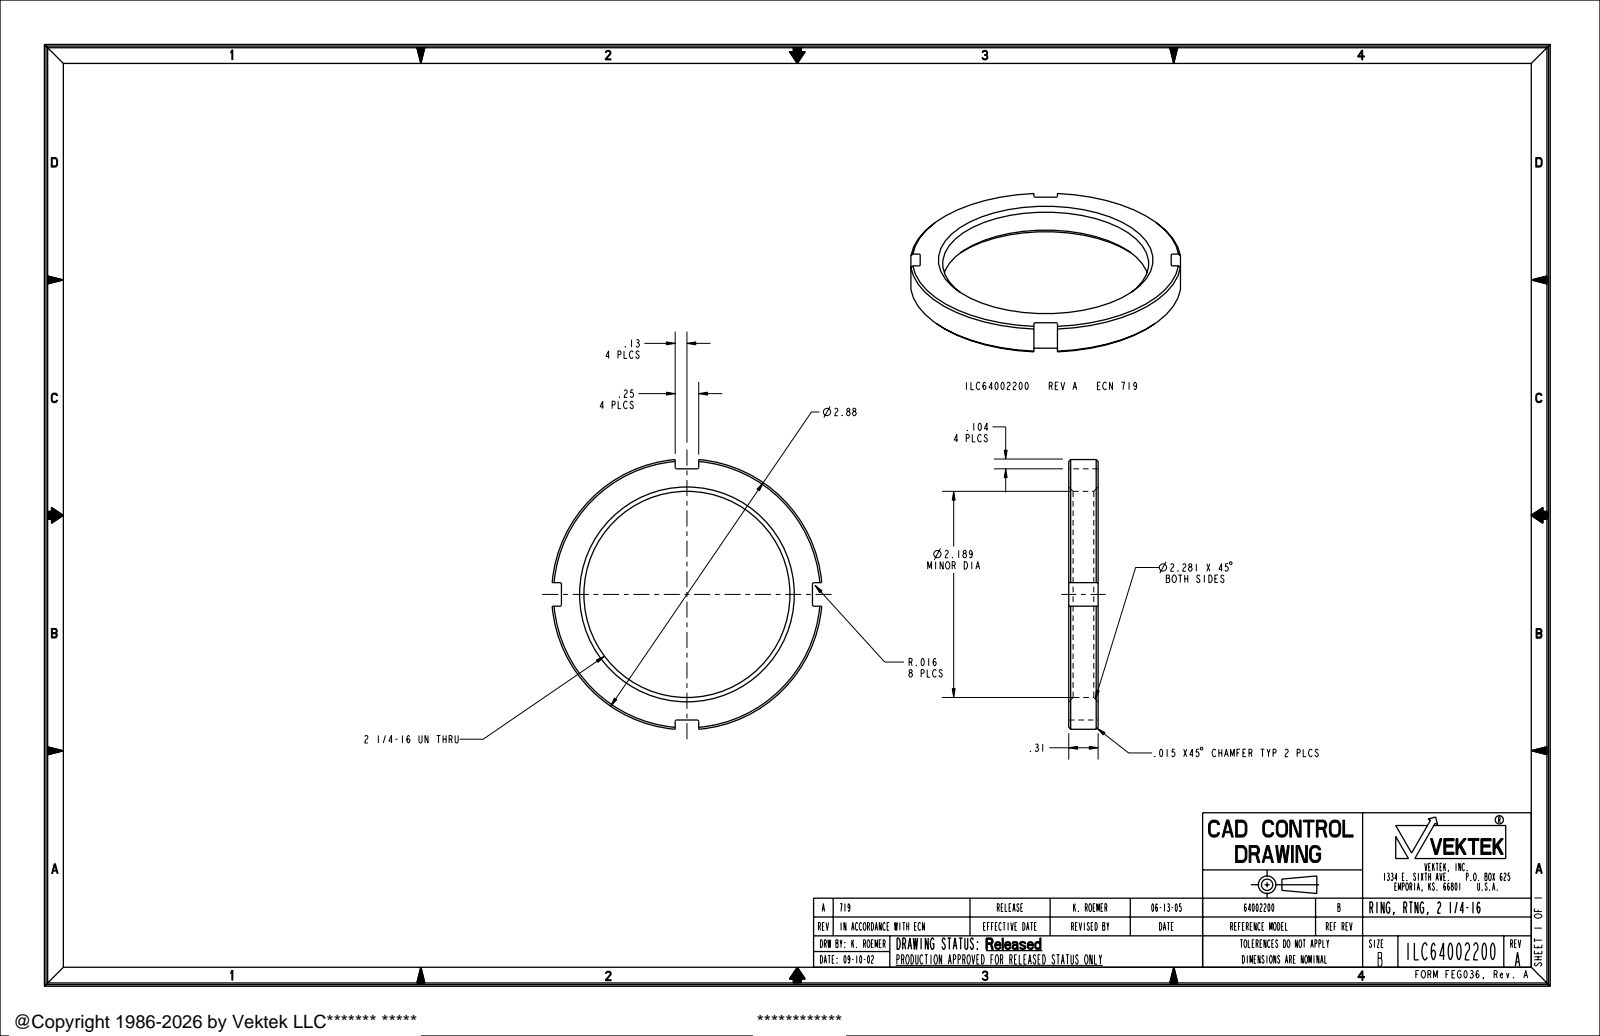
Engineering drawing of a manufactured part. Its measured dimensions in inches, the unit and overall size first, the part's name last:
Units: inches
Overall size (bounding box): 2.875 × 2.875 × 0.312
Round holes (diameter × count): ⌀2.189 ×1
Round bosses / shafts (diameter × count): ⌀2.875 ×1
Partial cylindrical surfaces — rounded edges, fillets, slot ends (radius × count): R0.016 ×8
Main face-to-face distances: 0.312, 1.209, 1.458, 2.667, 0.25
Volume: 0.801 in³ · Surface area: 9.883 in²
Bodies: 1 solid, 40 faces (14 planar, 14 cylindrical, 12 other)
Part name (STEP PRODUCT): ILC64002200
STEP written by: PRO/ENGINEER BY PARAMETRIC TECHNOLOGY CORPORATION, 2004290 (AUTOMOTIVE_DESIGN_CC2)
